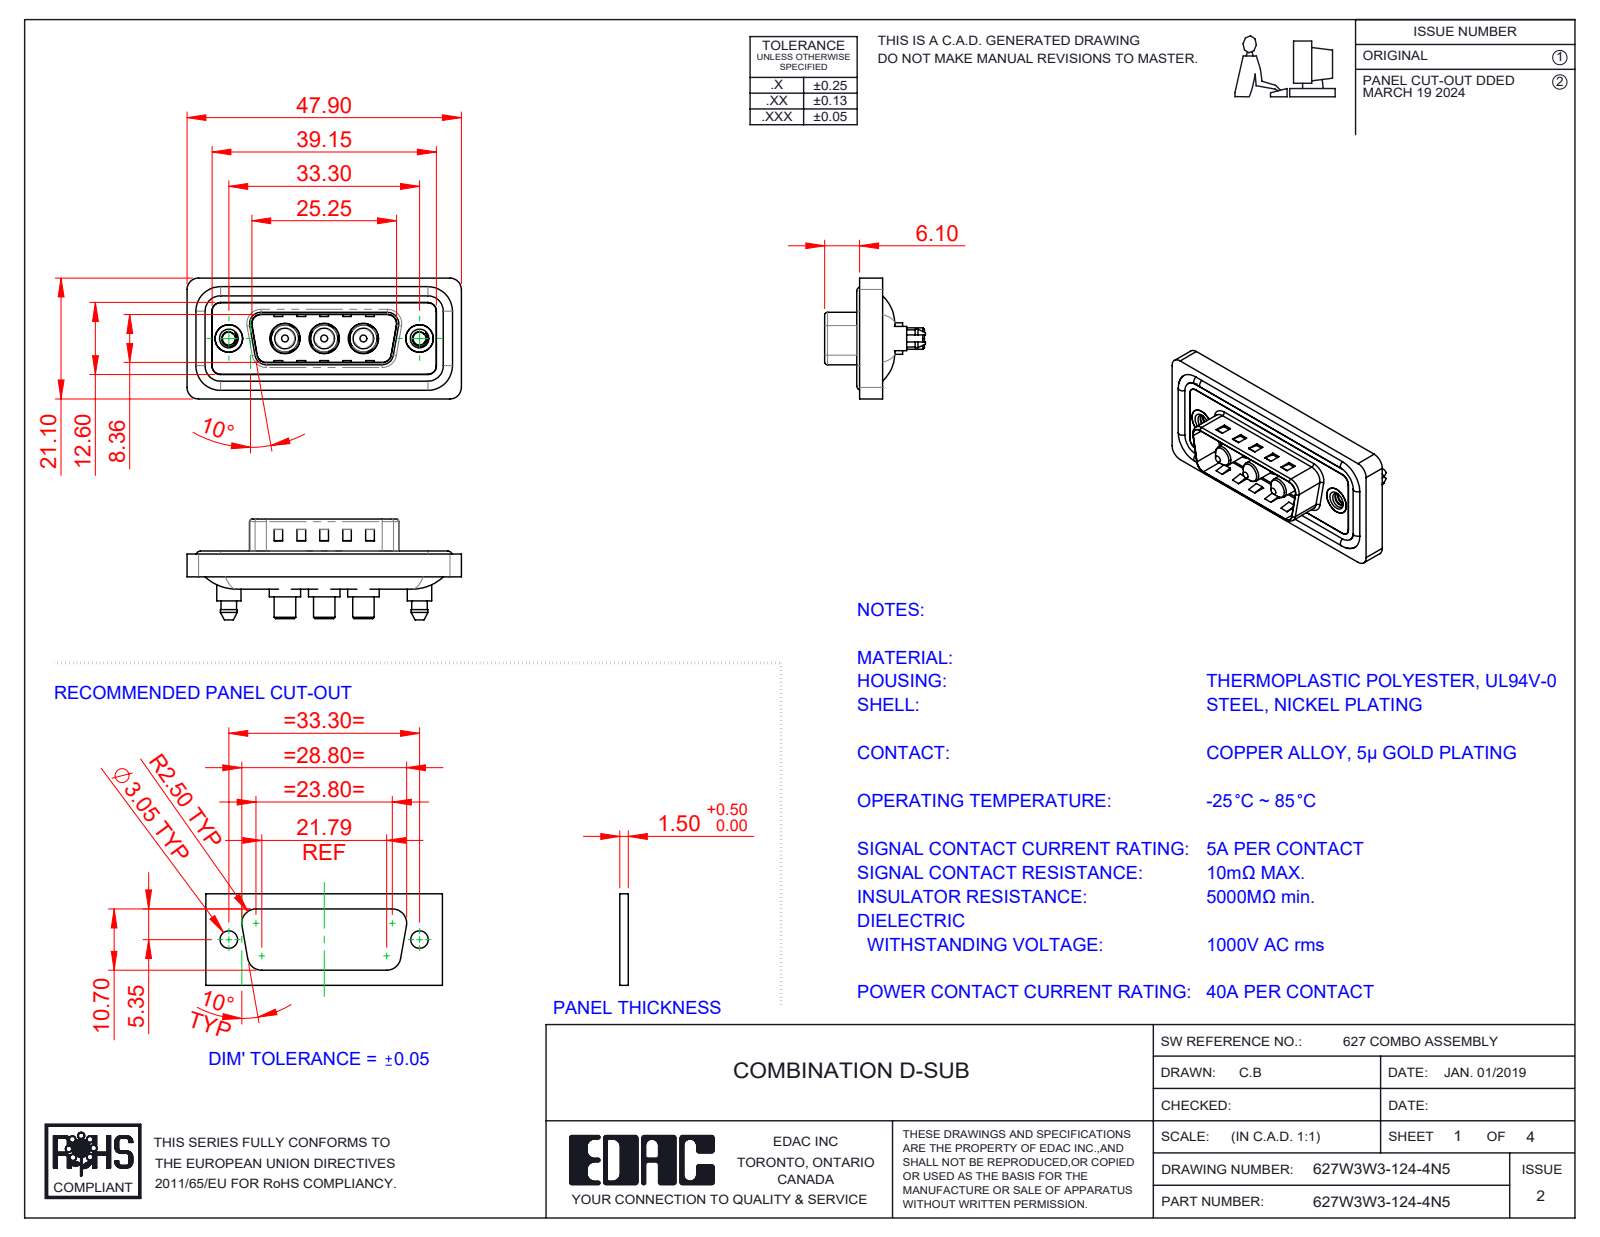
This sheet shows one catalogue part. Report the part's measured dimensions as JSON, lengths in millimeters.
{"part_name": "627Combo Shell Rear_15 Contacts; 627W3W3-124-4N5; 627Combo Waterproof Housing_15 Contacts; 627Combo Shell Front_15 Contacts (+3 more)", "step_written_by": "SolidWorks 2023 (CONFIG_CONTROL_DESIGN)", "units": "millimeters", "bodies": {"solids": 13, "faces": 614, "planar": 223, "cylindrical": 273, "other": 118}, "overall_size": [47.9, 21.1, 17.6], "volume_mm3": 5775, "surface_area_mm2": 9119, "round_holes": [[4.85, 3], [5.3, 3], [2.26, 2], [4, 2], [4.8, 2], [5, 2]], "round_bosses_or_shafts": [[1.6, 4], [5.5, 3], [5.2, 3], [4.75, 3], [3.75, 3], [3.6, 3], [5.4, 2], [4.9, 2]], "partial_cylinders_radius": [[1.5, 28], [2, 20], [1.6, 10], [0.5, 8], [0.25, 4], [0.6, 4], [0.65, 4], [0.9, 4]], "face_to_face_distances": [0.4, 1.1, 3.1, 1.5, 1.6, 0.5, 2.9, 4, 0.7, 0.82], "hole_center_spacings": [6.85, 9.8, 16.65, 23.5, 13.7, 33.3]}
